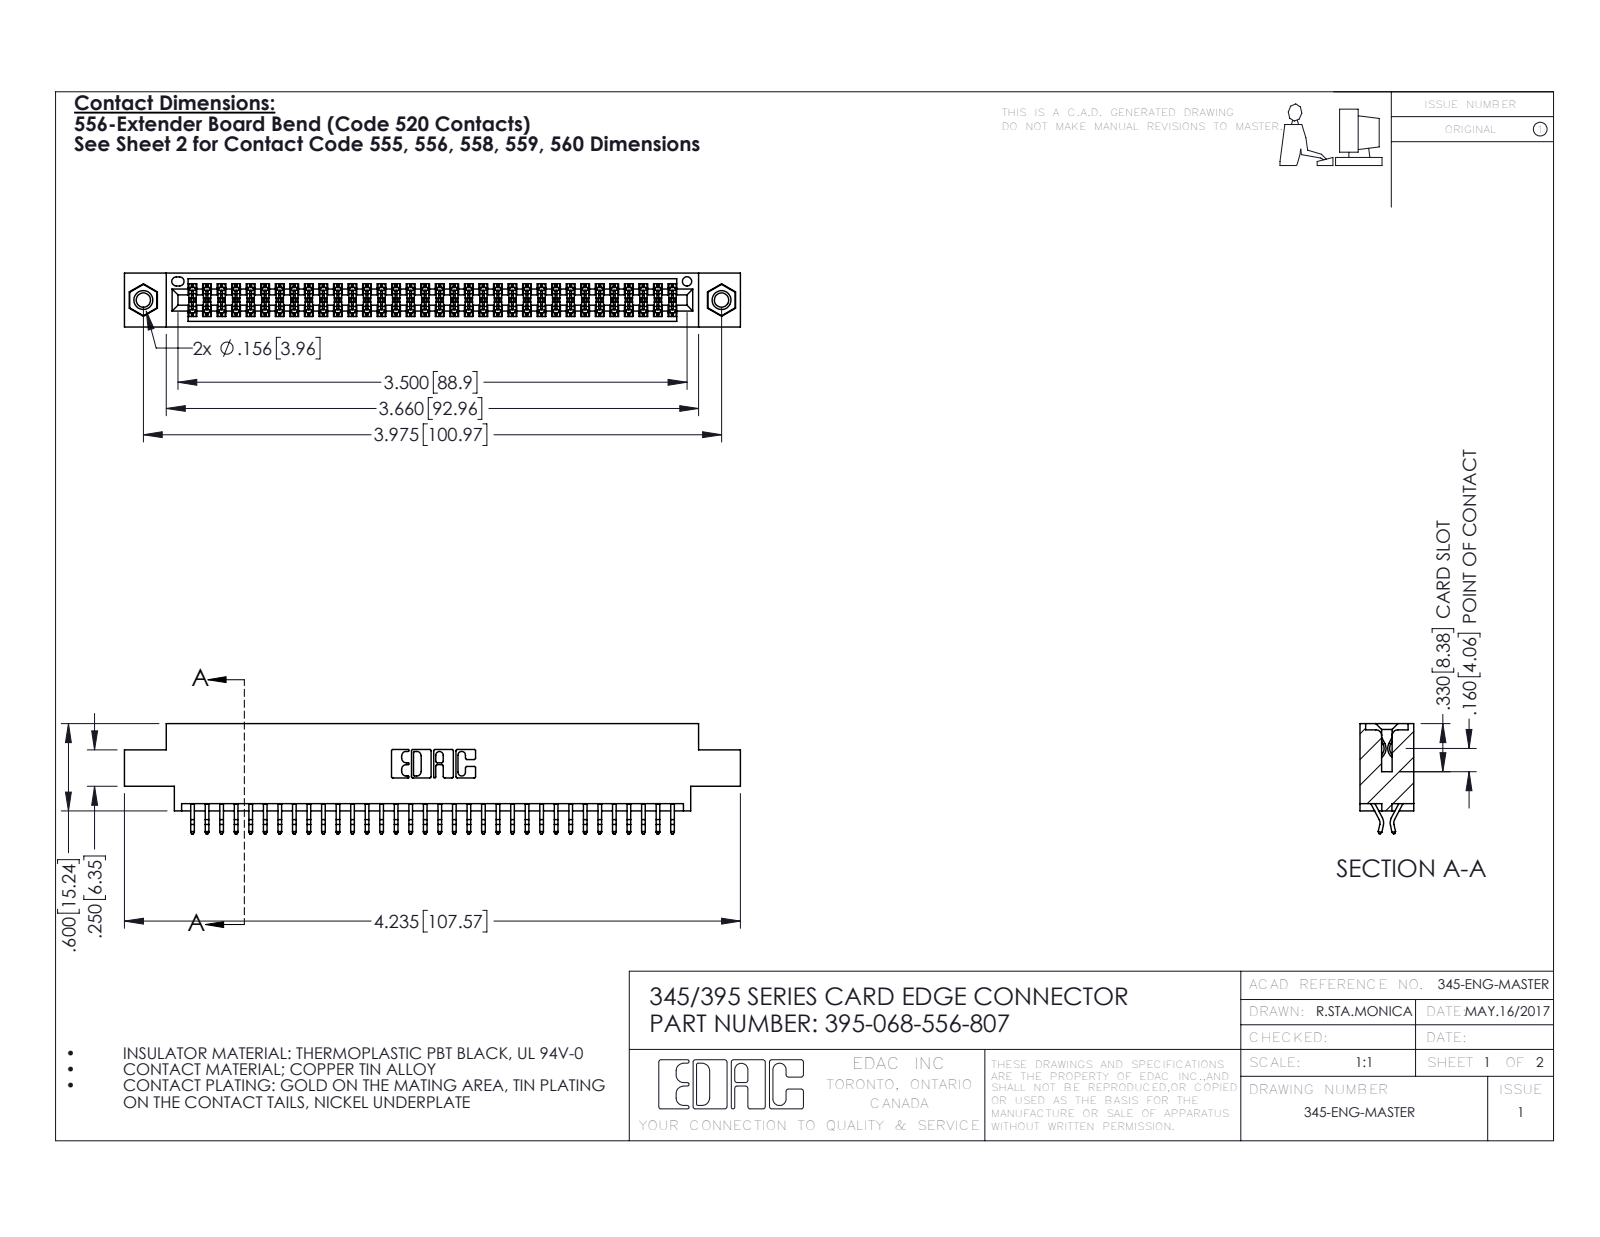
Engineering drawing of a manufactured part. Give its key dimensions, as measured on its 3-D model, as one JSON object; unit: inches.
{"part_name": "345-250-001_345-250-005-103; 345 Part_0.170 Offset - 0.156 Dia-TI; 395-068-556-807; 345-292-001_556 Tail", "step_written_by": "SolidWorks 2016 (CONFIG_CONTROL_DESIGN)", "units": "inches", "bodies": {"solids": 71, "faces": 3998, "planar": 2632, "cylindrical": 1350, "other": 16}, "overall_size": [4.235, 0.757, 0.37], "volume_in3": 0.625, "surface_area_in2": 23.41, "round_holes": [[0.098, 2], [0.125, 2], [0.156, 2], [0.064, 1]], "round_bosses_or_shafts": [[0.155, 2]], "partial_cylinders_radius": [[0.006, 102], [0.01, 22], [0.007, 6], [0.031, 6], [0.026, 3], [0.01, 2], [0.014, 2], [0.019, 2]], "face_to_face_distances": [0.072, 0.298, 0.37, 0.2, 0.025, 0.098, 0.272, 0.225, 0.175, 0.149], "hole_center_spacings": [0.27, 3.74, 3.975]}
